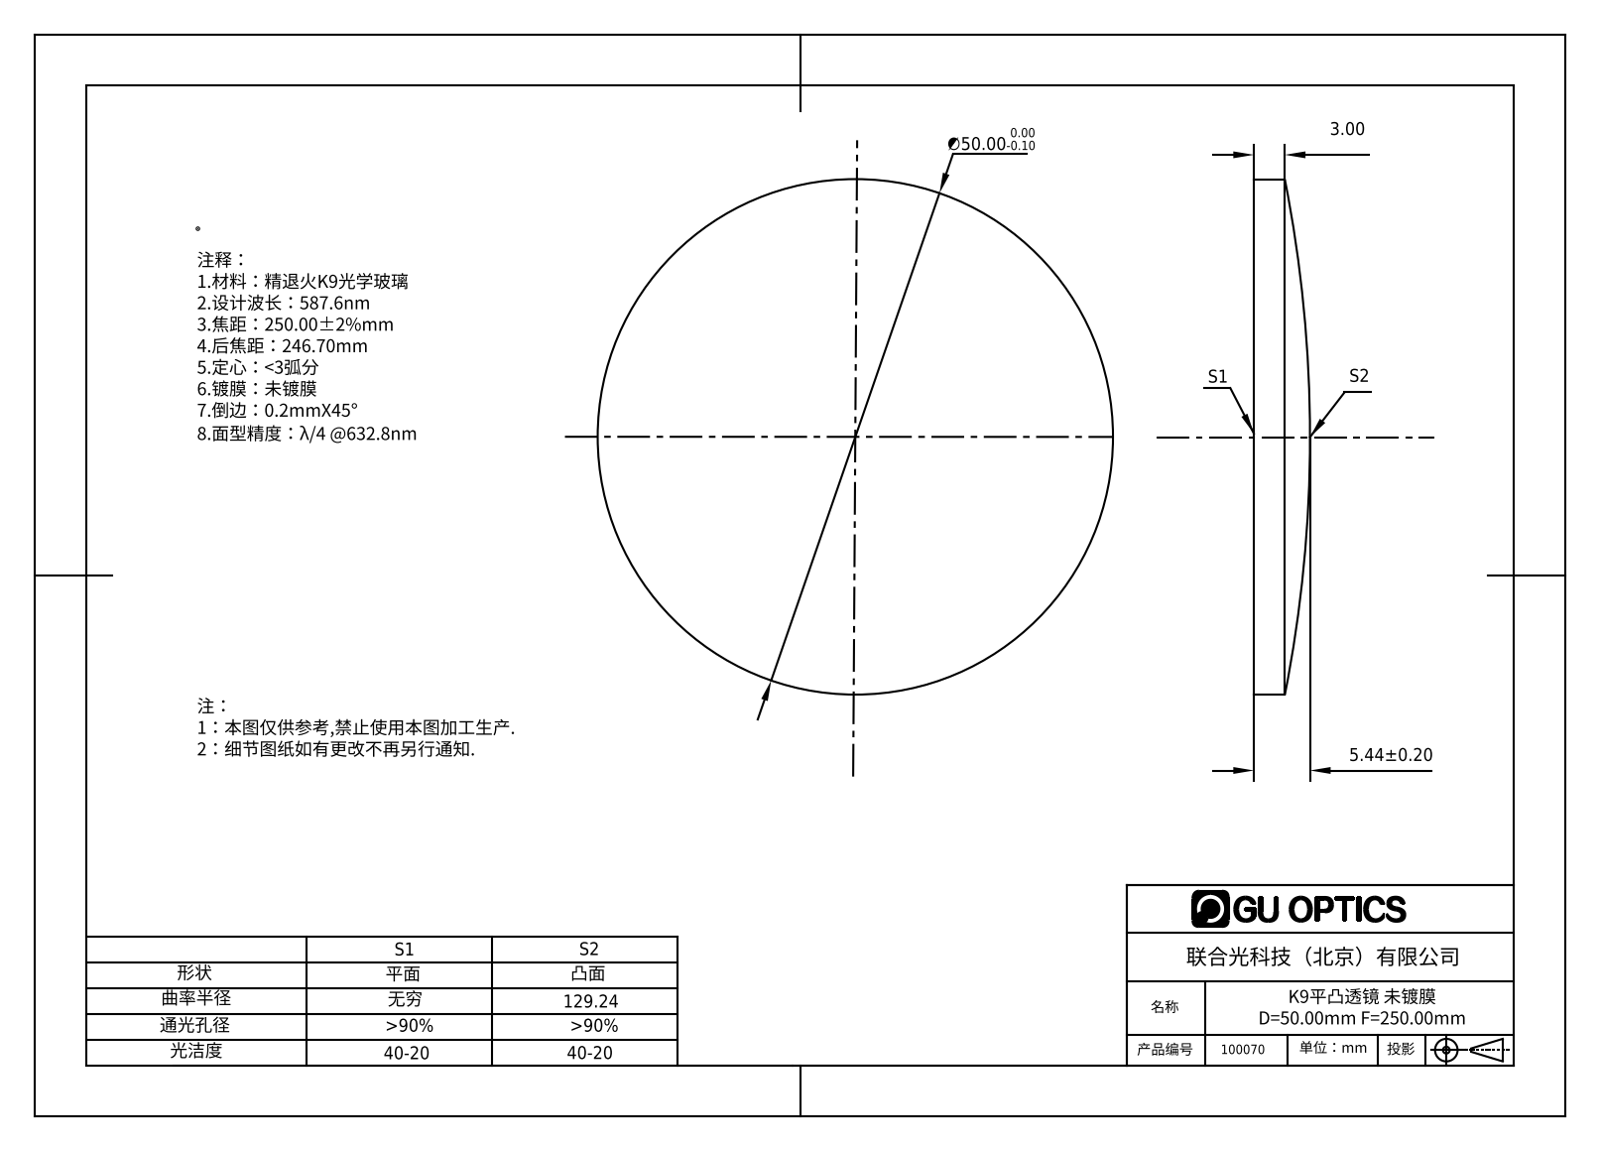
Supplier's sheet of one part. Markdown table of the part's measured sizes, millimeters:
| quantity | value |
| --- | --- |
| part name | 100070 |
| STEP written by | SolidWorks 2016 (AUTOMOTIVE_DESIGN) |
| units | millimeters |
| bodies | 1 solid, 5 faces (1 planar, 2 cylindrical, 2 other) |
| overall size | 50 × 50 × 5.44 |
| volume | 8 294 mm³ |
| surface area | 4 417 mm² |
| round bosses / shafts (diameter × count) | 50 × 1 |
